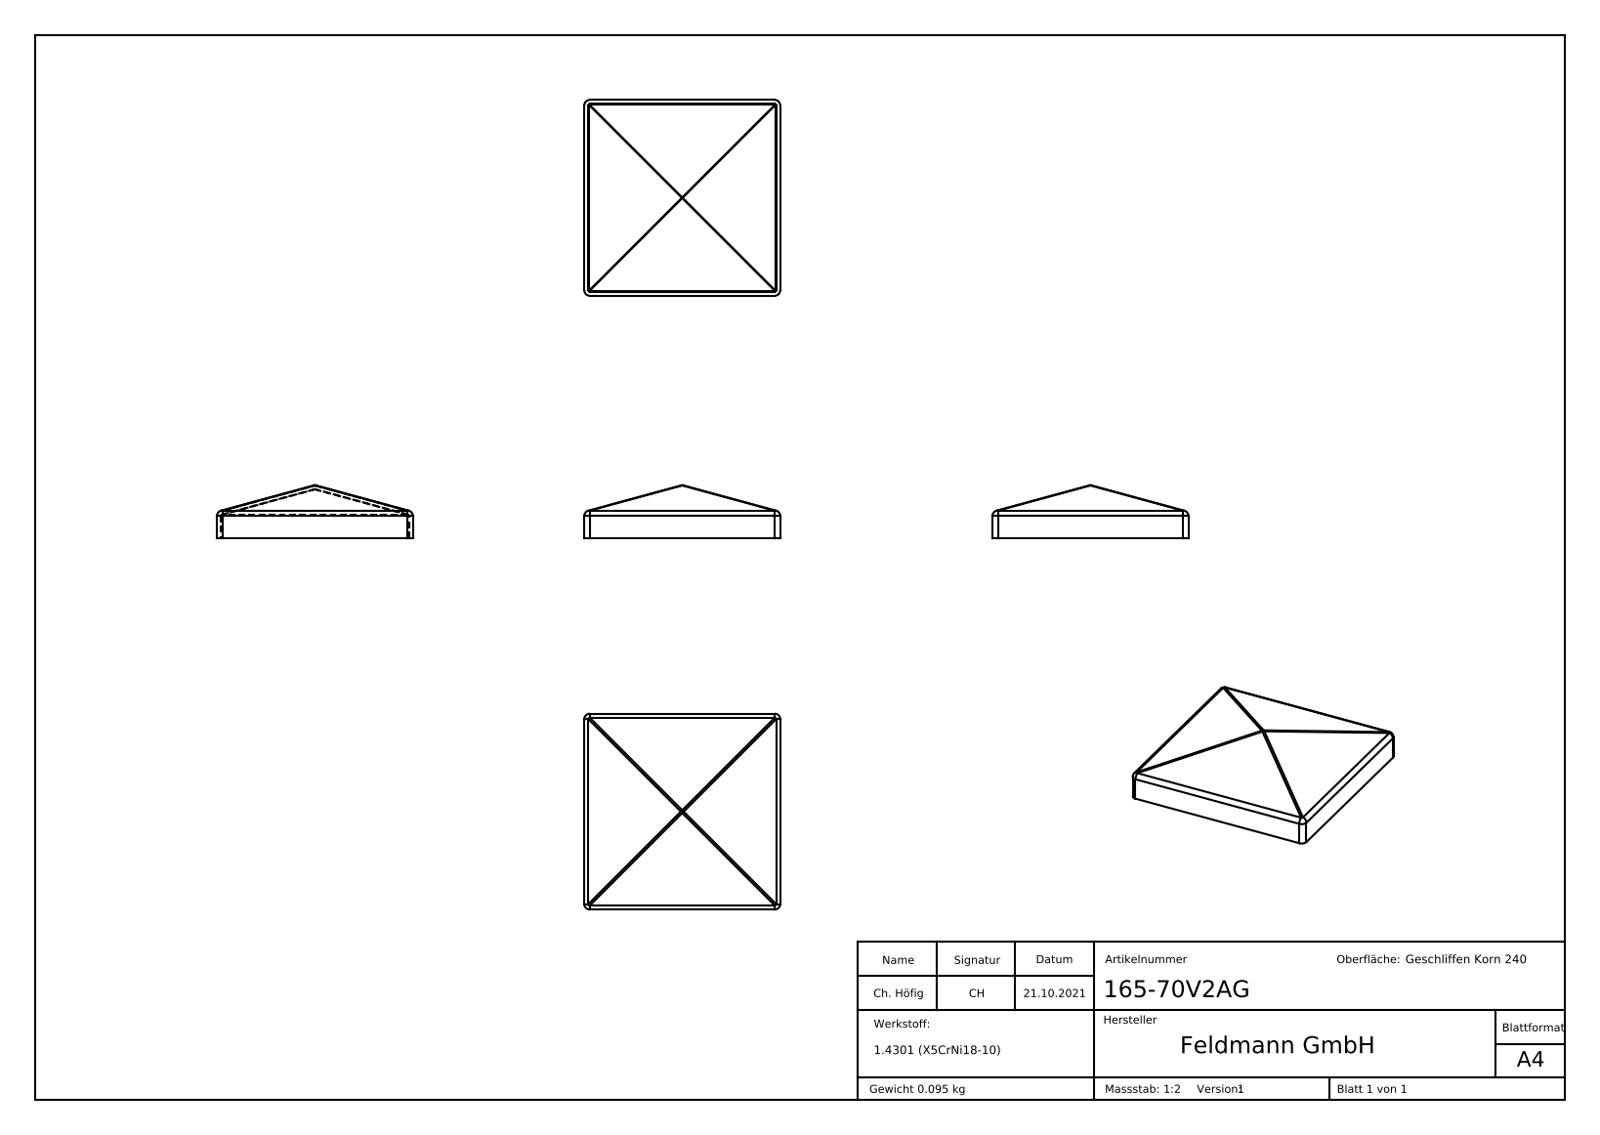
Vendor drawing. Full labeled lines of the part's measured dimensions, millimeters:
Part name (STEP PRODUCT): 165-70V2AG
STEP written by: SolidWorks 2018 (CONFIG_CONTROL_DESIGN)
Units: millimetres
Bodies: 1 solid, 271 faces (148 planar, 24 cylindrical, 99 other)
Overall size (bounding box): 73.5 × 73.5 × 19.93
Volume: 11 978 mm³ · Surface area: 16 411 mm²
Partial cylindrical surfaces — rounded edges, fillets, slot ends (radius × count): R0.5 ×12, R2 ×12
Main face-to-face distances: 1.5, 72, 73.5, 70.5, 1.4, 70.6, 72.1, 0.45, 1.66, 1.78
